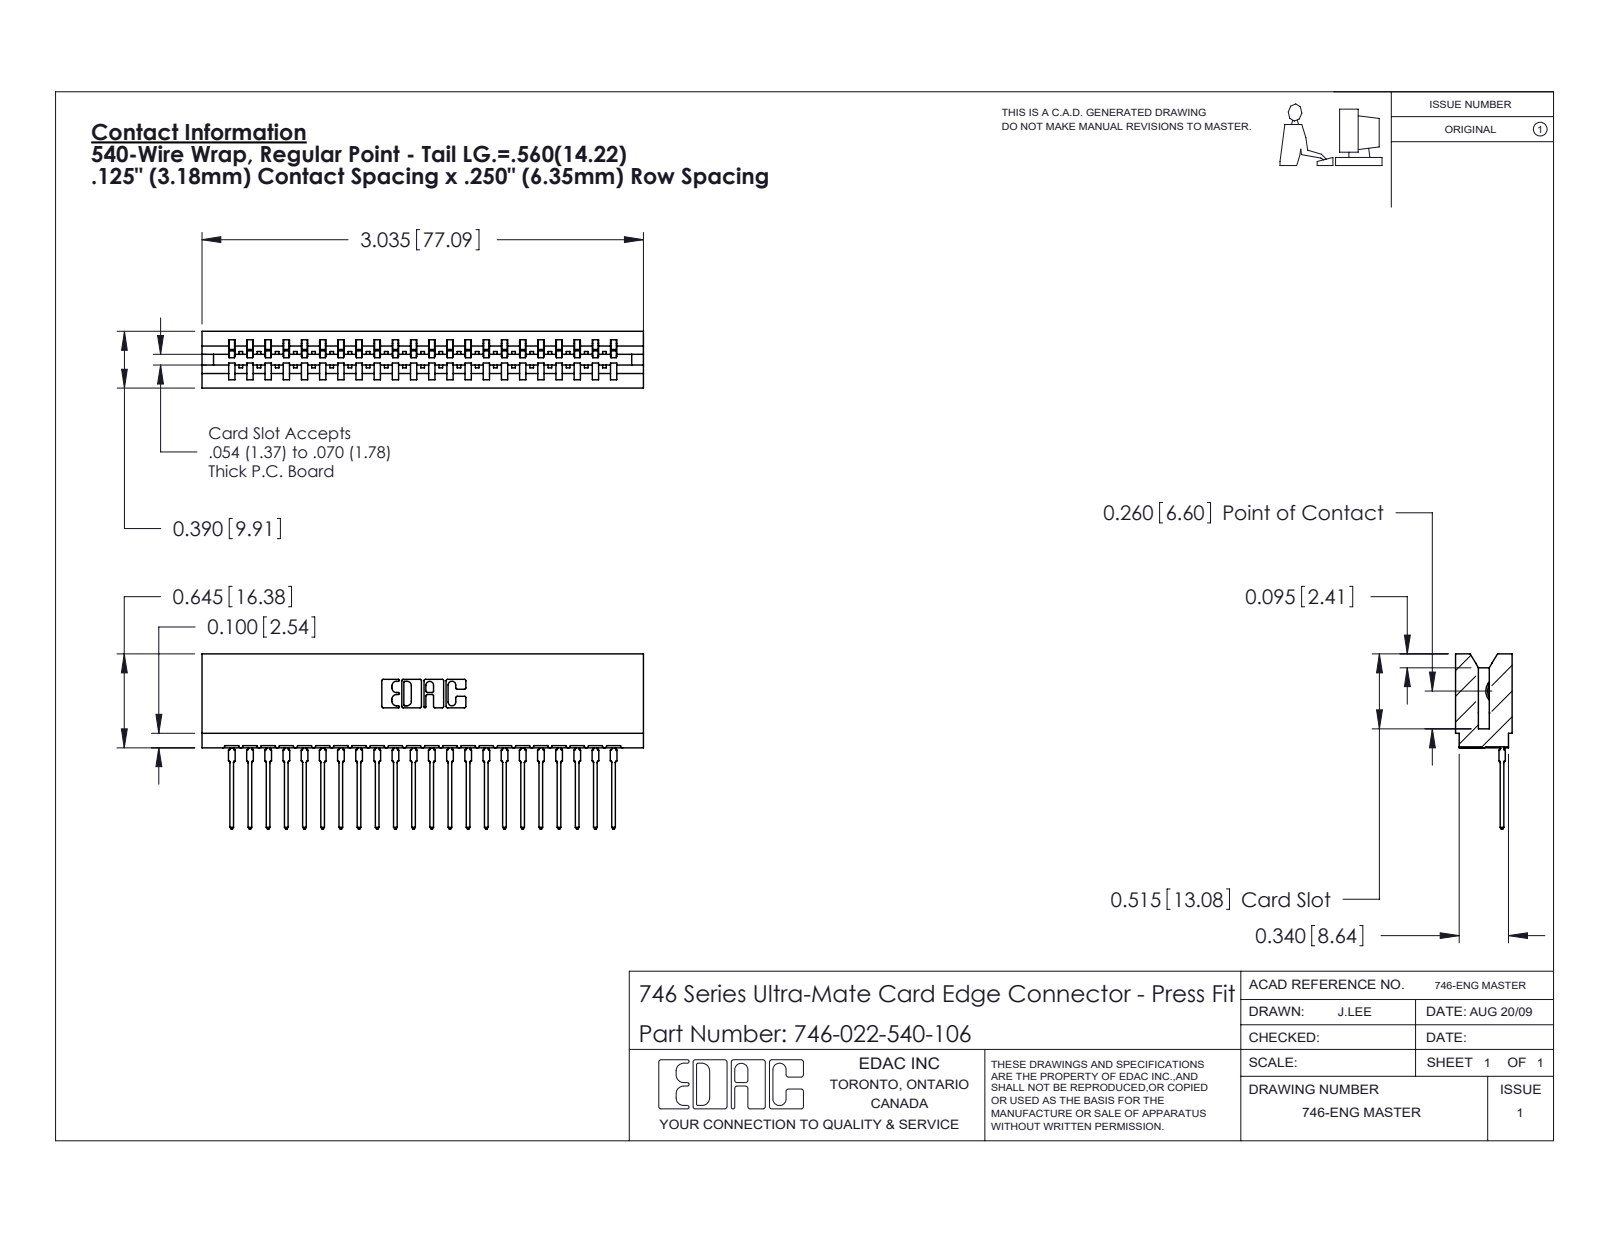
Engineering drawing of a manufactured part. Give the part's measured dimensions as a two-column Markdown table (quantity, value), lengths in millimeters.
| quantity | value |
| --- | --- |
| part name | 746 Part_.515 Slot Depth - 06; 746-292-001_540; 746-022-540-106 |
| STEP written by | SolidWorks 2020 (CONFIG_CONTROL_DESIGN) |
| units | millimeters |
| bodies | 23 solids, 2474 faces (1442 planar, 460 cylindrical, 572 other) |
| overall size | 77.1 × 30.6 × 9.9 |
| volume | 8 230 mm³ |
| surface area | 12 130 mm² |
| partial cylindrical surfaces (radius × count) | 0.5 × 44, 0.4 × 23, 0.3 × 22, 0.2 × 6, 0.8 × 6, 0.1 × 4, 0.3 × 4, 0.7 × 3 |
| main face-to-face distances | 8.5, 1.4, 6.4, 9.9, 12.7, 0.6, 7.8, 2.1, 1.1, 3.2 |
